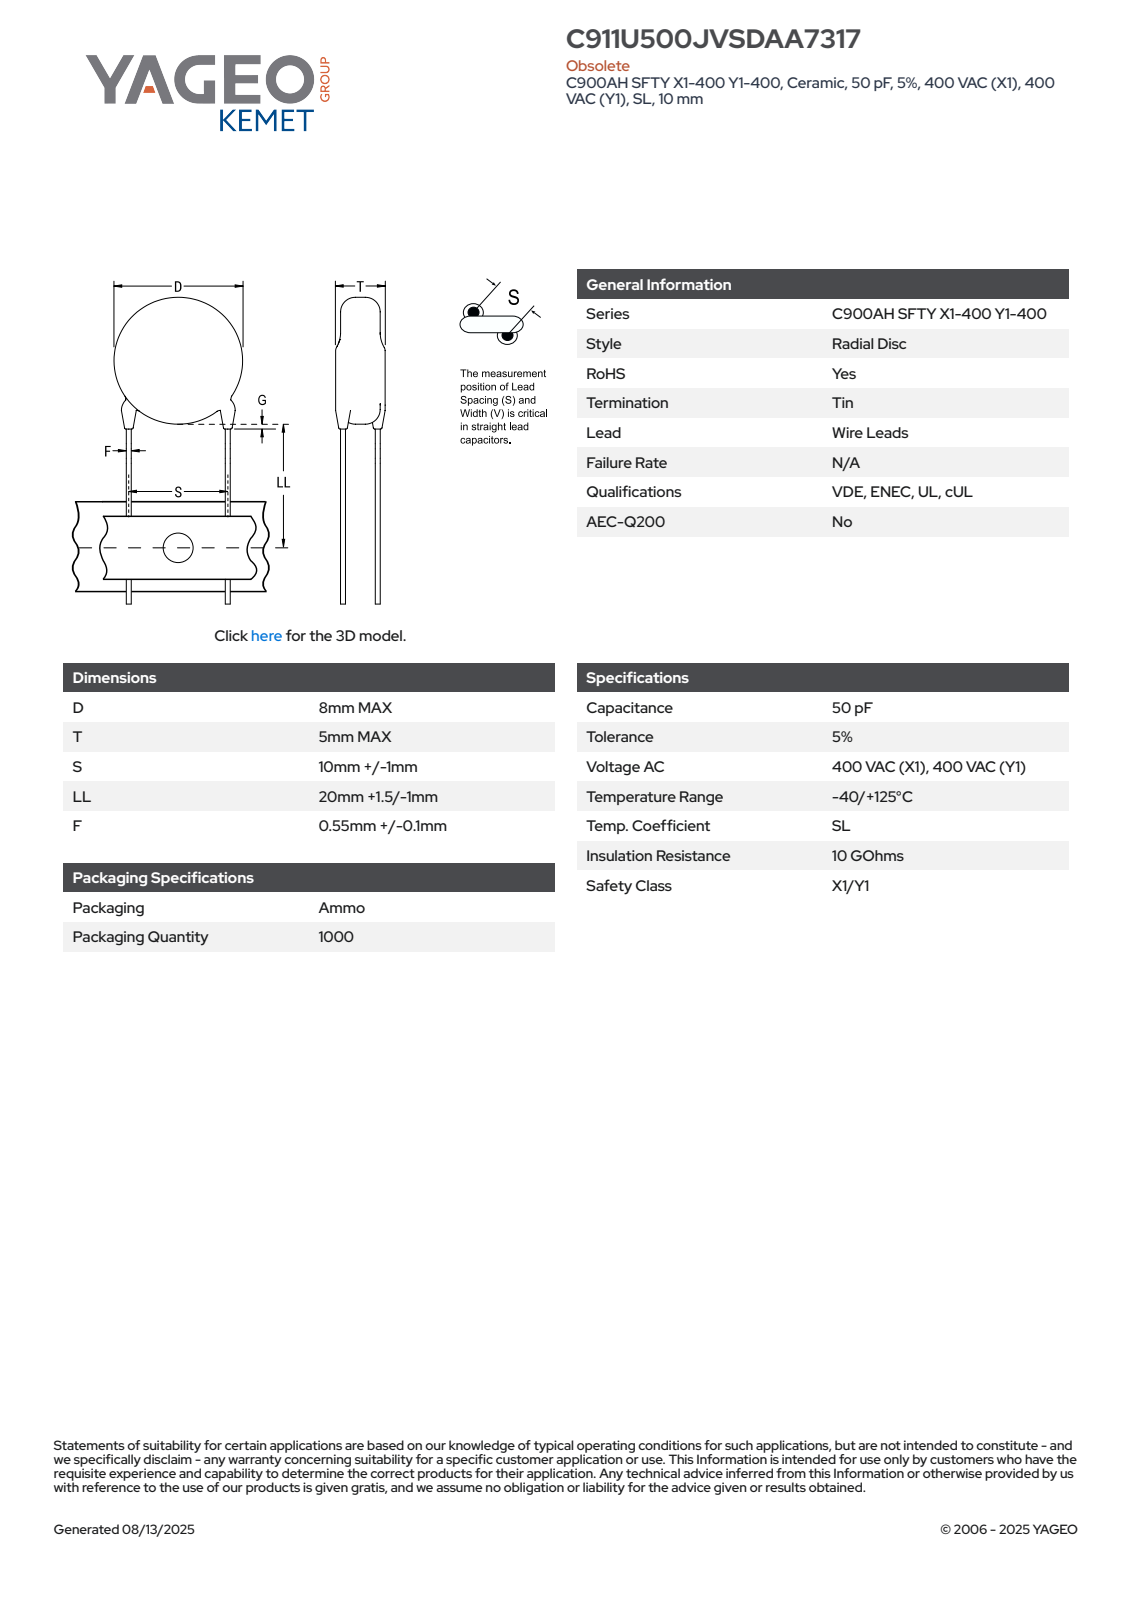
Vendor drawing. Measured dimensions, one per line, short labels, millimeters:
name: CCD_STC900_D8T5S10LL21.5F0.65G3
written by: SolidWorks 2014 (AUTOMOTIVE_DESIGN)
unit: mm
bodies: 4 solids, 83 faces (61 planar, 6 cylindrical, 16 other)
size: 29.5 × 9.42 × 5.95
volume: 260 mm³; area: 310 mm²
bosses: 2× ⌀0.65, 1× ⌀8
face distances: 5, 25.96, 25.04, 0.92, 0.4, 1.04, 3.77, 0.57, 2.73, 2.84
